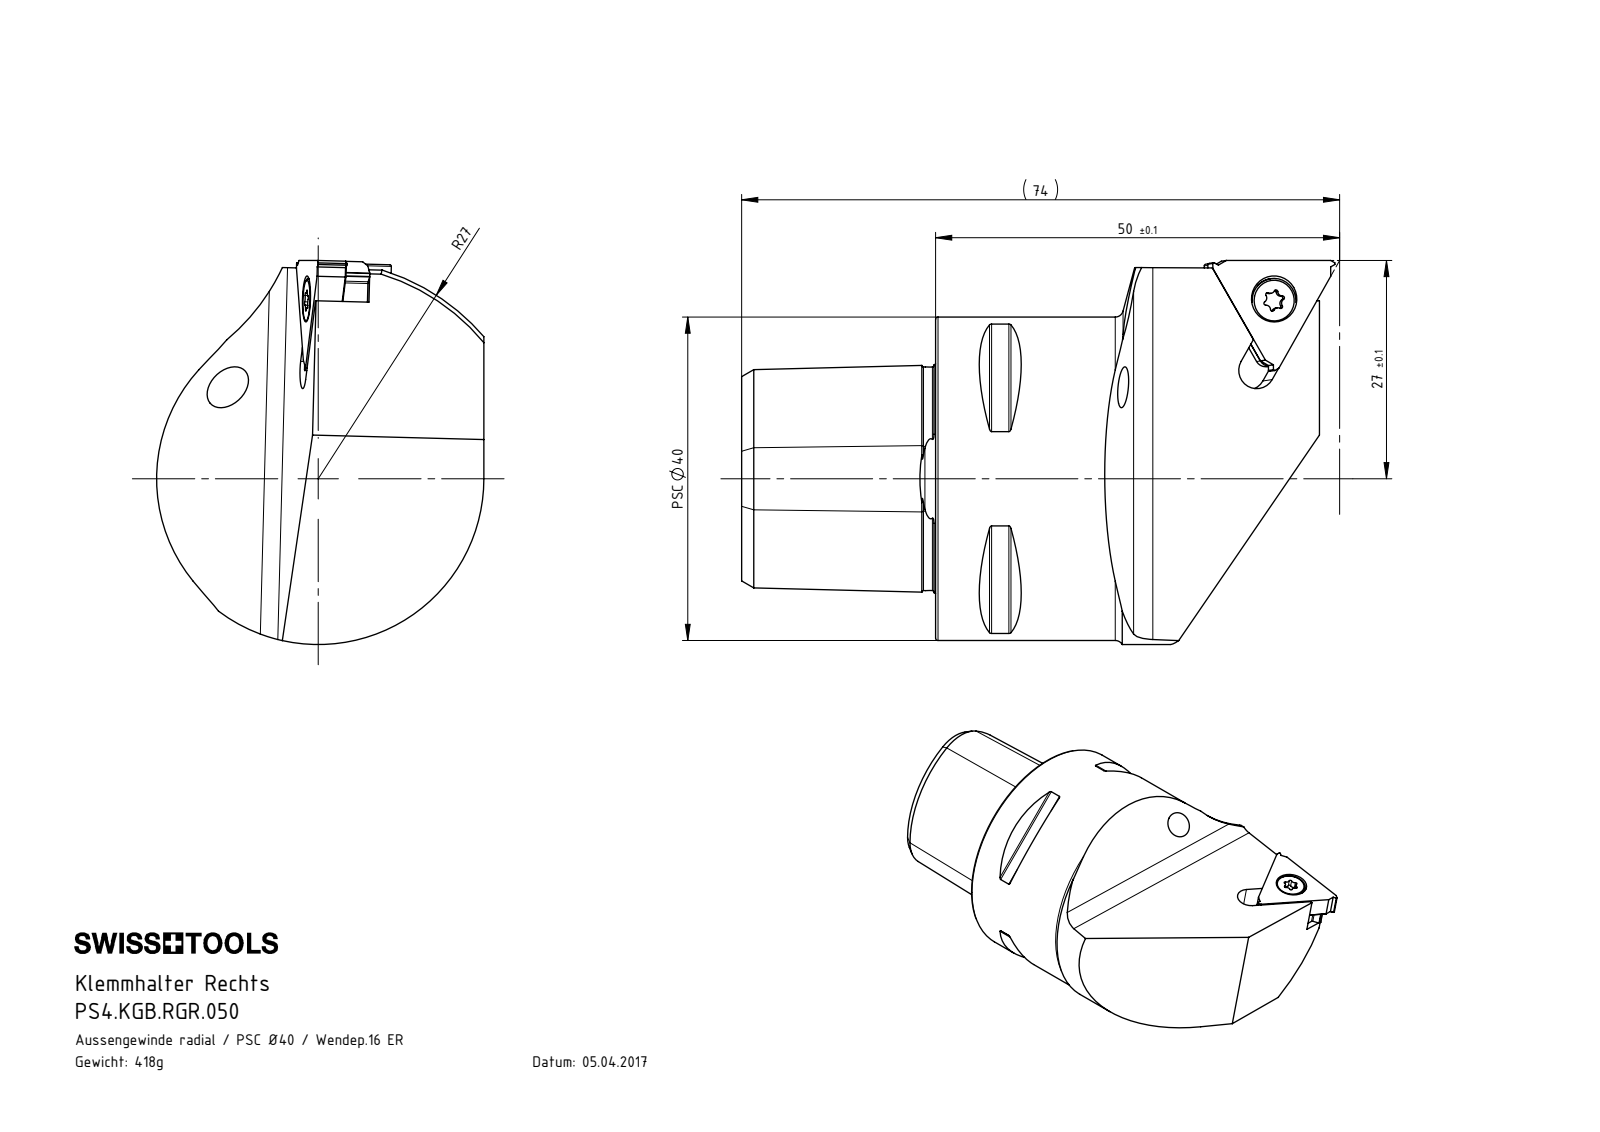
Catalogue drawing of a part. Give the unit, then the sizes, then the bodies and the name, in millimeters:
Units: millimetres
Overall size (bounding box): 73.41 × 47.5 × 40.5
Round holes (diameter × count): ⌀4 ×3, ⌀2.58 ×2, ⌀4.2 ×2, ⌀4.02 ×1, ⌀4.6 ×1, ⌀5 ×1, ⌀12.5 ×1, ⌀18 ×1, ⌀20 ×1
Round bosses / shafts (diameter × count): ⌀5.5 ×2, ⌀40 ×1, ⌀5 ×1, ⌀3.18 ×1, ⌀3 ×1, ⌀2.78 ×1
Partial cylindrical surfaces — rounded edges, fillets, slot ends (radius × count): R0.3 ×8, R0.23 ×6, R0.34 ×6, R0.57 ×6, R0.57 ×6, R0.1 ×2, R3 ×2, R0.25 ×1
Main face-to-face distances: 3.45, 3.2, 24, 6.65, 15.52, 6.85, 3.65, 35.3, 15, 9
Hole centre spacings: 23.5, 460.09, 460.14
Volume: 51 704 mm³ · Surface area: 13 604 mm²
Bodies: 7 solids, 246 faces (89 planar, 66 cylindrical, 91 other)
Part name (STEP PRODUCT): WGB-ER2.102.003_A; KVT_MB_600_050; WGB-ER3.001.007_A; PS4-KGB.RGR.050_A_Fertigbearbeitung (+3 more)
STEP written by: SolidWorks 2017 (AUTOMOTIVE_DESIGN)
